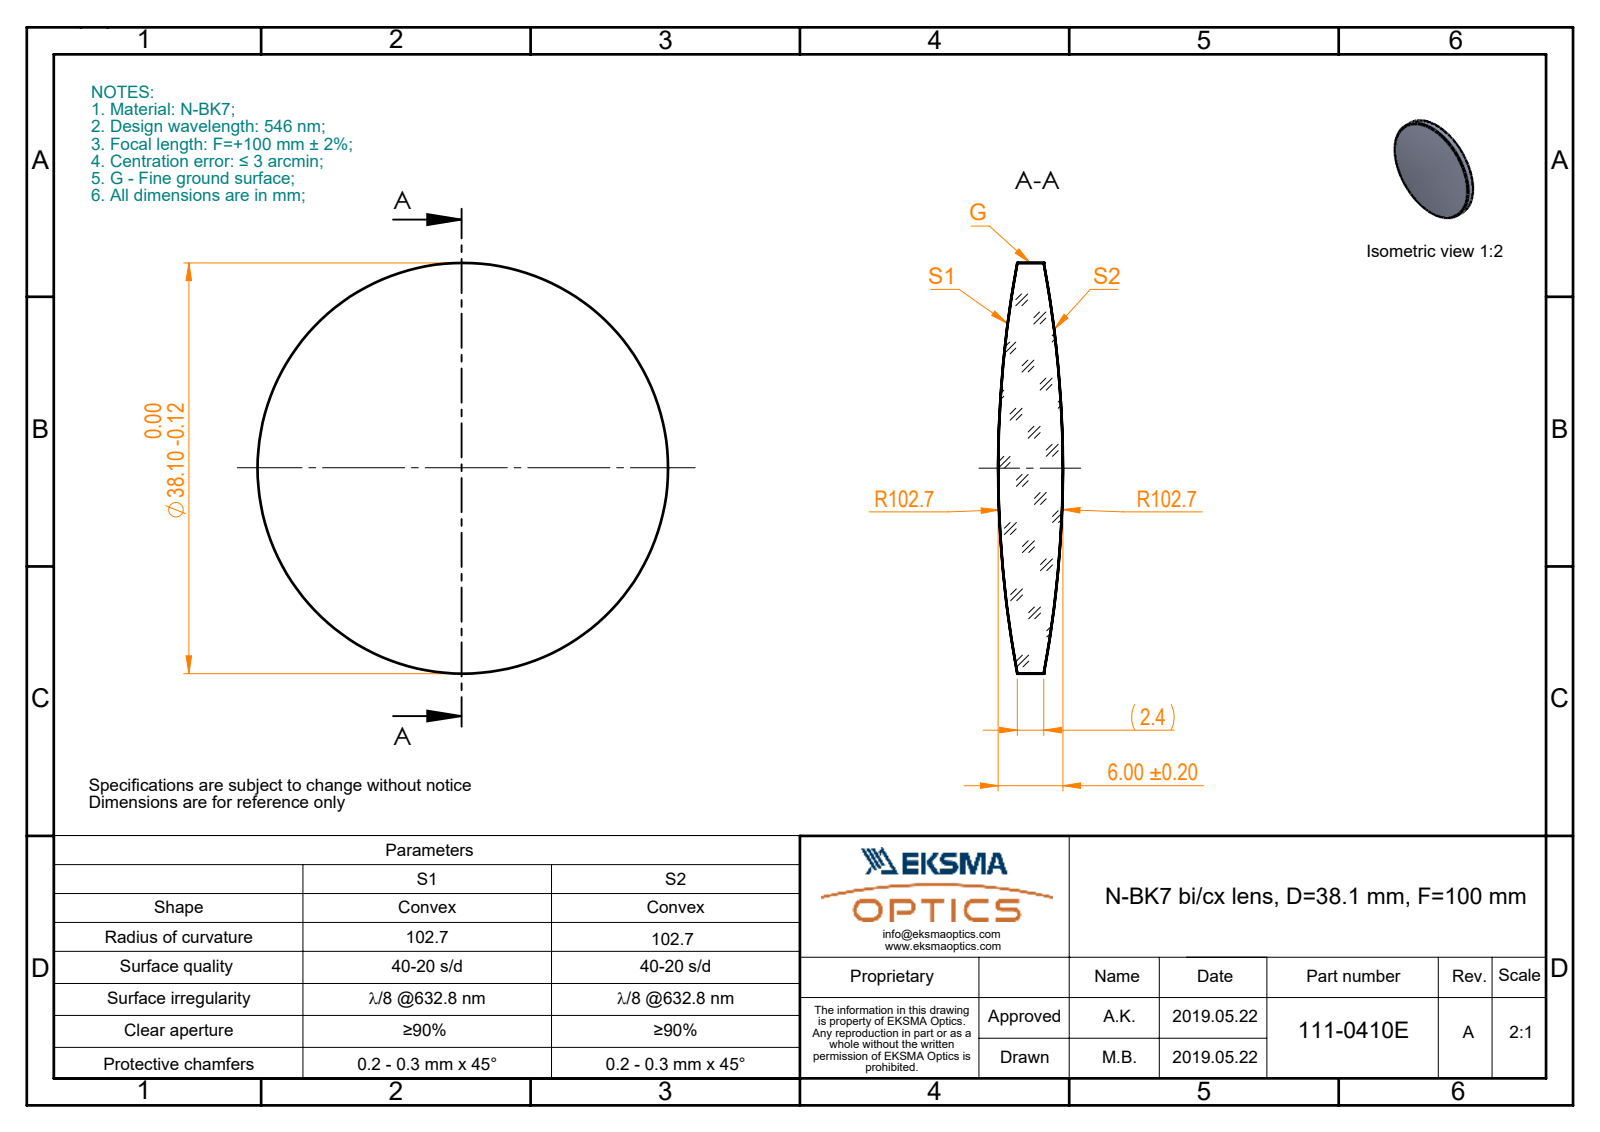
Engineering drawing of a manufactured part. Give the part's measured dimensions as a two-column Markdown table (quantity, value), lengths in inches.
| quantity | value |
| --- | --- |
| part name | 111-0410E BK7 bi-cx 38.1 F100 |
| STEP written by | SolidWorks 2017 (CONFIG_CONTROL_DESIGN) |
| units | inches |
| bodies | 1 solid, 6 faces (0 planar, 2 cylindrical, 4 other) |
| overall size | 1.5 × 1.5 × 0.236 |
| volume | 0.294 in³ |
| surface area | 4.018 in² |
| round bosses / shafts (diameter × count) | 1.5 × 1 |
